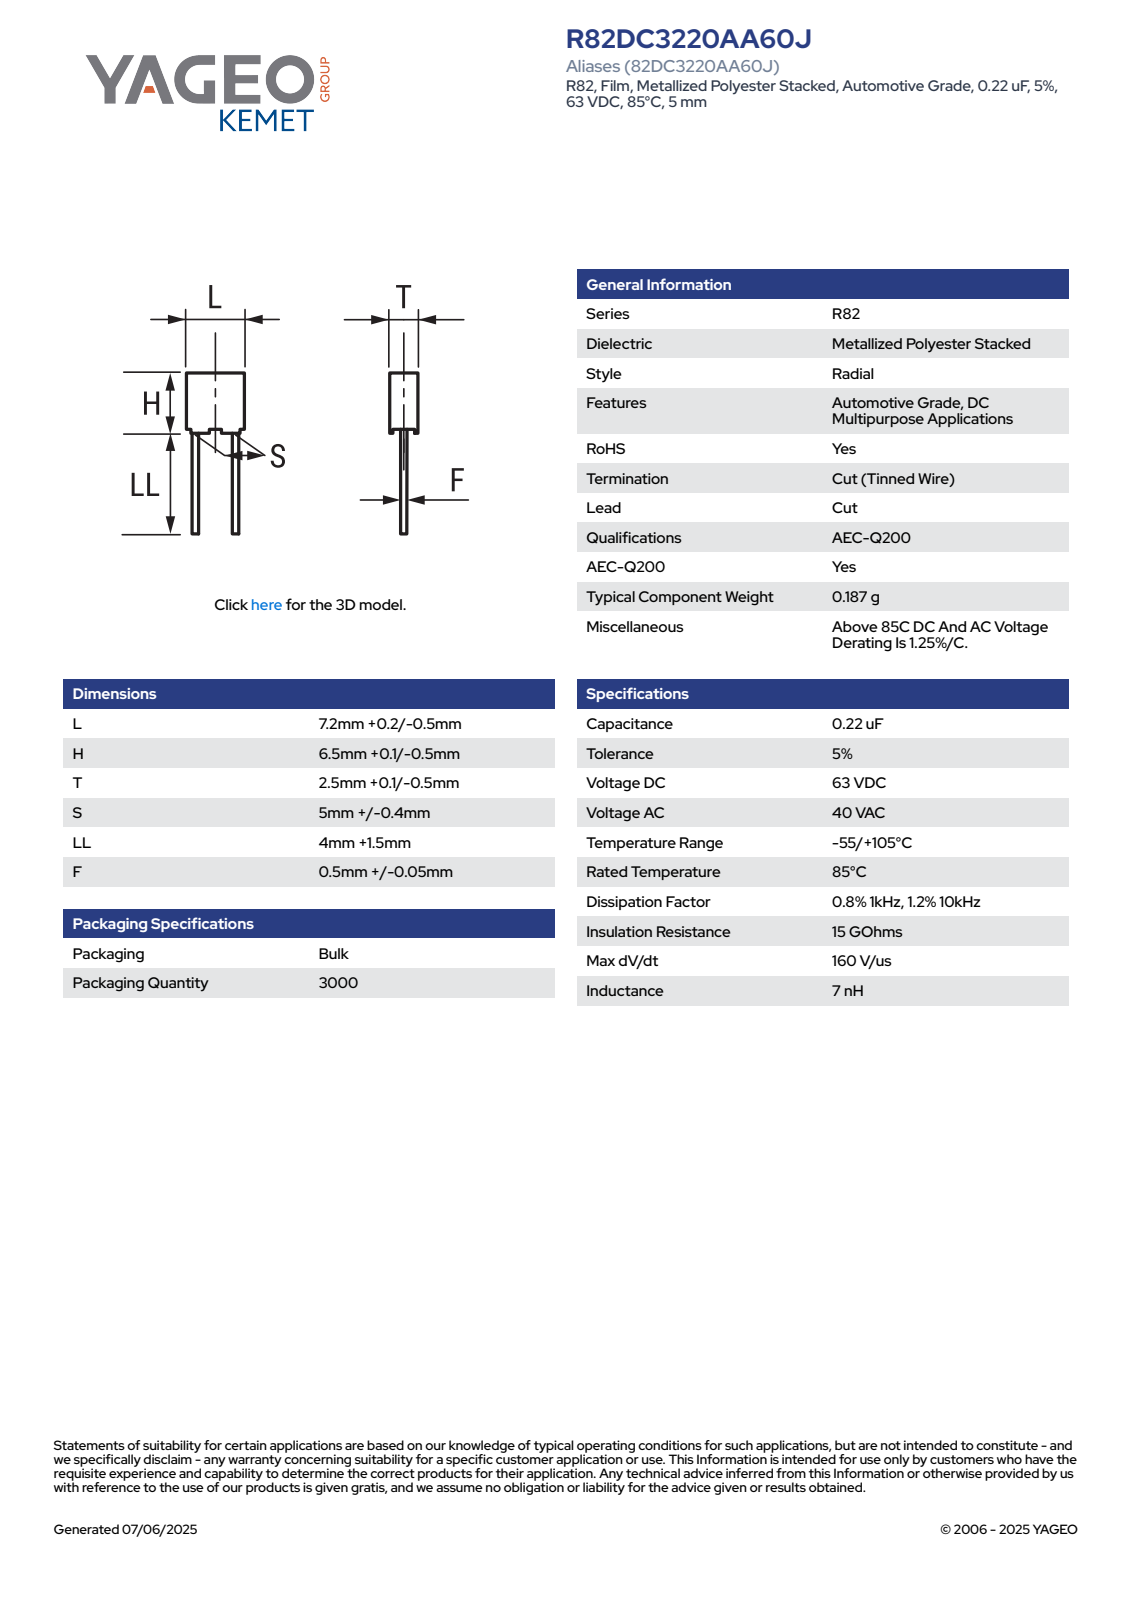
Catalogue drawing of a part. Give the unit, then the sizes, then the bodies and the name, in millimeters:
Units: millimetres
Overall size (bounding box): 12.1 × 7.4 × 2.6
Round bosses / shafts (diameter × count): ⌀0.55 ×2
Partial cylindrical surfaces — rounded edges, fillets, slot ends (radius × count): R0.5 ×4
Main face-to-face distances: 2.6, 7.4, 5.85, 2.35, 2.1, 0.75, 6.6, 7.15, 6.9, 0.52
Volume: 118 mm³ · Surface area: 204 mm²
Bodies: 4 solids, 85 faces (77 planar, 8 cylindrical, 0 other)
Part name (STEP PRODUCT): CFR_RB3_7.2X6.5X2.5_L7.4H6.6T2.6S5LL5.5F0.55
STEP written by: SolidWorks 2014 (AUTOMOTIVE_DESIGN)
